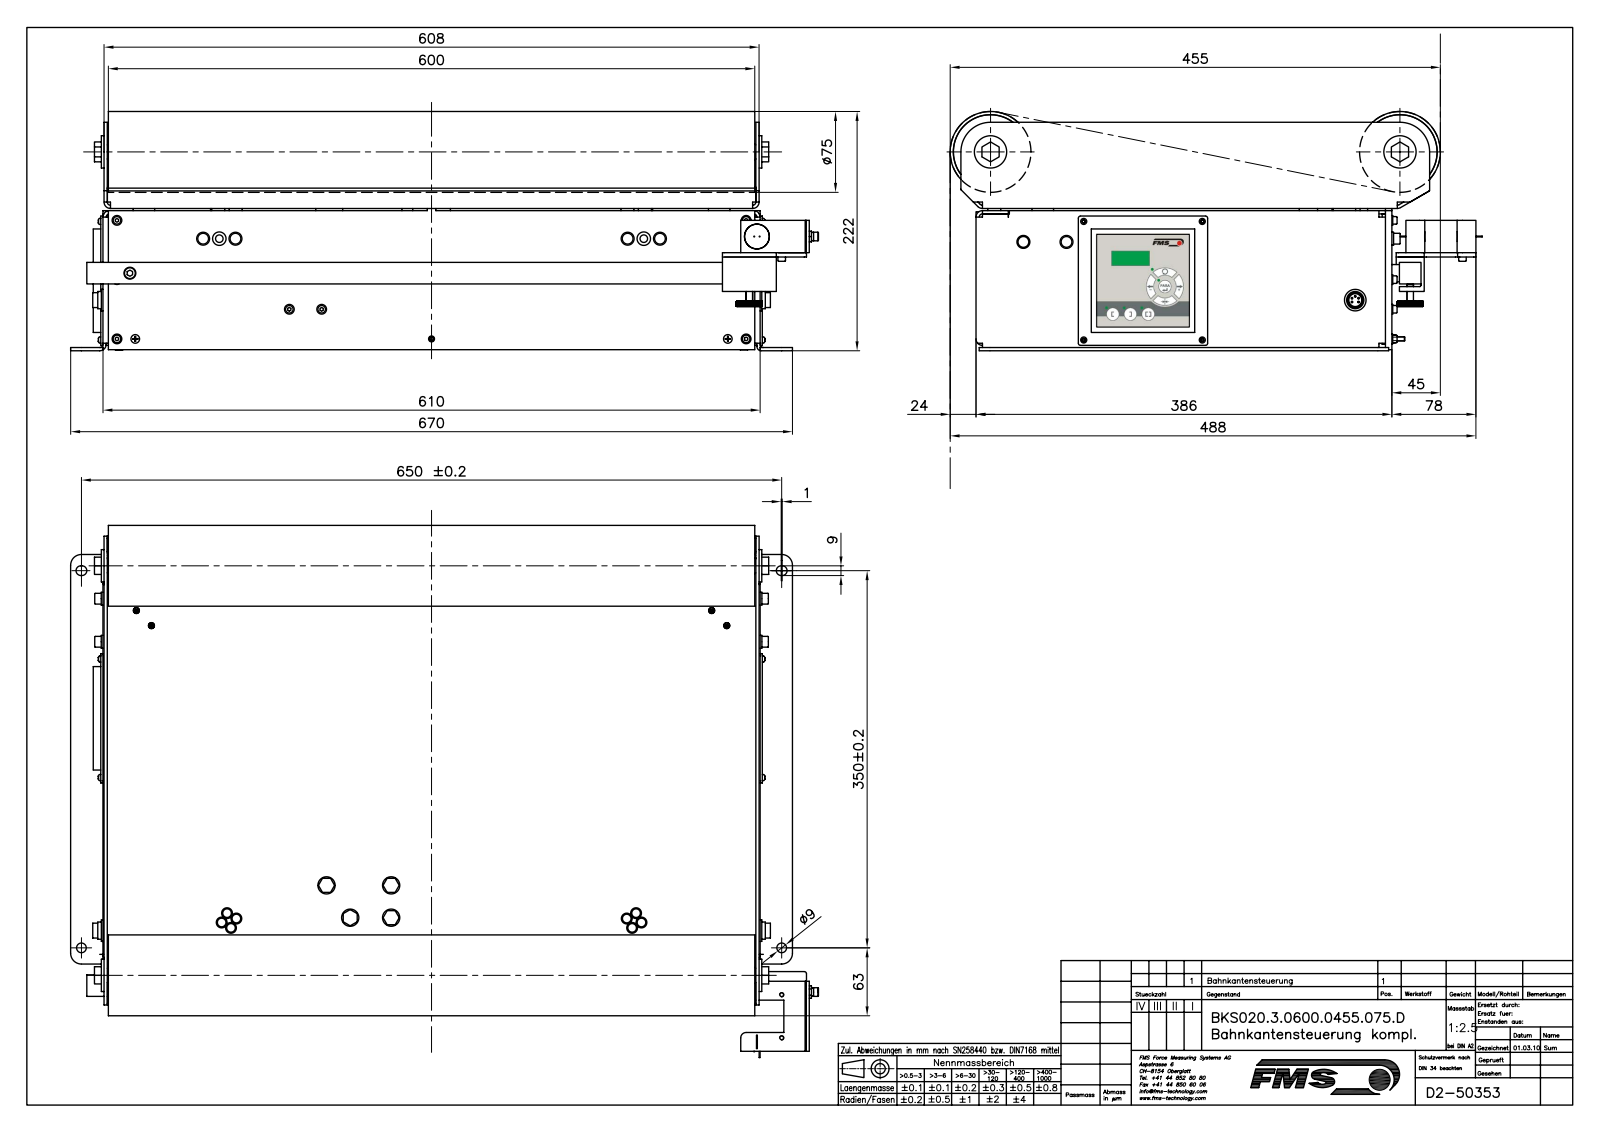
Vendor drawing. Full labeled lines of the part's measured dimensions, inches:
Part name (STEP PRODUCT): K50353; K49789; K49790; TEIL1 (+8 more)
STEP written by: Mechanical Desktop 2007 (CONFIG_CONTROL_DESIGN)
Units: inches
Bodies: 176 solids, 6098 faces (3738 planar, 1872 cylindrical, 488 other)
Overall size (bounding box): 27.327 × 19.213 × 8.74
Volume: 287.1 in³ · Surface area: 4 464 in²
Round holes (diameter × count): ⌀0.118 ×30, ⌀0.126 ×14, ⌀0.169 ×14, ⌀0.135 ×13, ⌀0.252 ×10, ⌀0.087 ×8, ⌀0.102 ×8, ⌀0.209 ×8, ⌀0.138 ×7, ⌀0.236 ×6, ⌀0.331 ×6, ⌀0.039 ×4
Round bosses / shafts (diameter × count): ⌀0.394 ×20, ⌀0.157 ×18, ⌀0.315 ×15, ⌀0.236 ×15, ⌀0.472 ×10, ⌀0.276 ×10, ⌀0.118 ×10, ⌀0.354 ×8
Partial cylindrical surfaces — rounded edges, fillets, slot ends (radius × count): R0.013 ×48, R0.079 ×30, R0.039 ×29, R0.01 ×24, R0.022 ×24, R0.008 ×20, R0.01 ×19, R0.118 ×15
Main face-to-face distances: 0.118, 0.039, 5, 5.118, 5.039, 5.157, 0.079, 23.858, 0.157, 0.197
Hole centre spacings: 3.287, 0.394, 3.836, 3.853, 4.331, 3.268, 0.028, 0.463
